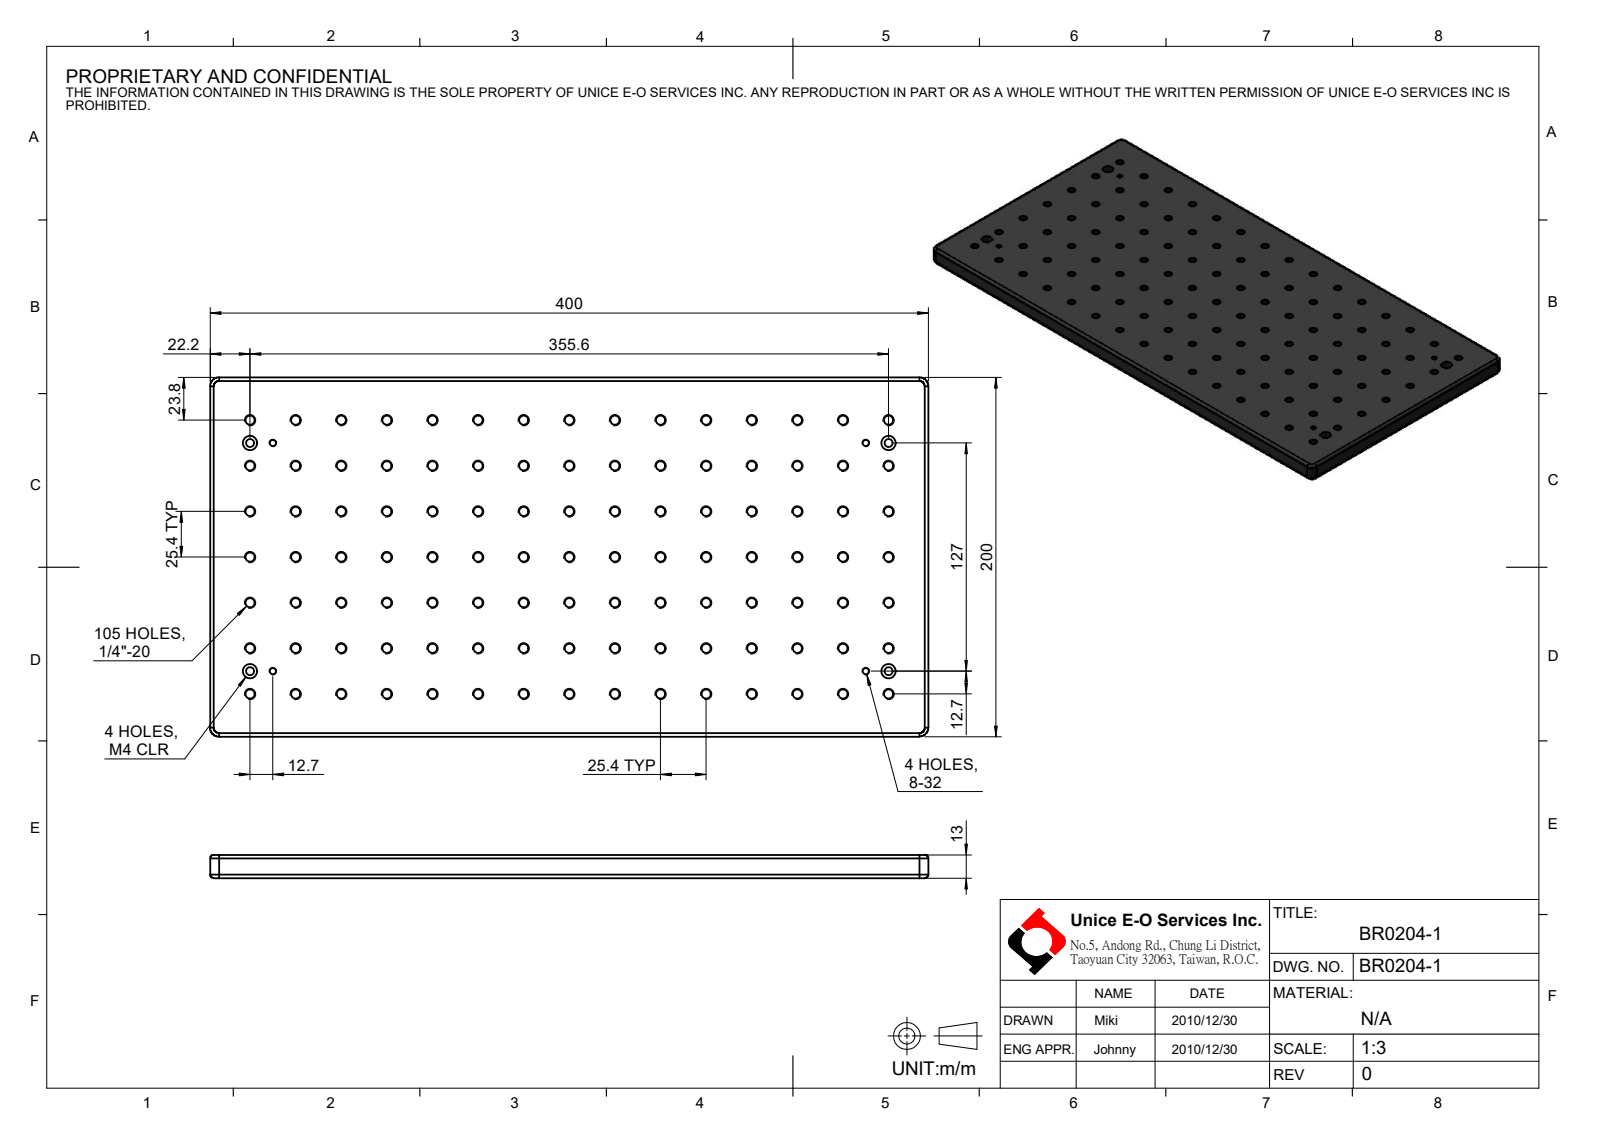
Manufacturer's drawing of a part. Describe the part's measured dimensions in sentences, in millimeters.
The part is named "BR0204-1". Its 3-D file was written by "SolidWorks 2016 (CONFIG_CONTROL_DESIGN)". It is 1 solid with 264 faces: 10 planar, 246 cylindrical and 8 other. Overall it measures 400 by 200 by 13 millimeters. Its volume is 1 008 000 cubic millimeters and its surface area 192 352 square millimeters. Round holes: 105 of diameter 5.11, 4 of diameter 3.45, 4 of diameter 4.5, 4 of diameter 8. Partial cylindrical surfaces (rounded edges, fillets, slot ends): 8 of radius 2, 4 of radius 5. The main face-to-face distances are 13, 200, 400, 7, 6. The hole center spacings are 25.4, 50.8, 127, 154.5, 76.2, 160.64, 152.4, 170.39.
